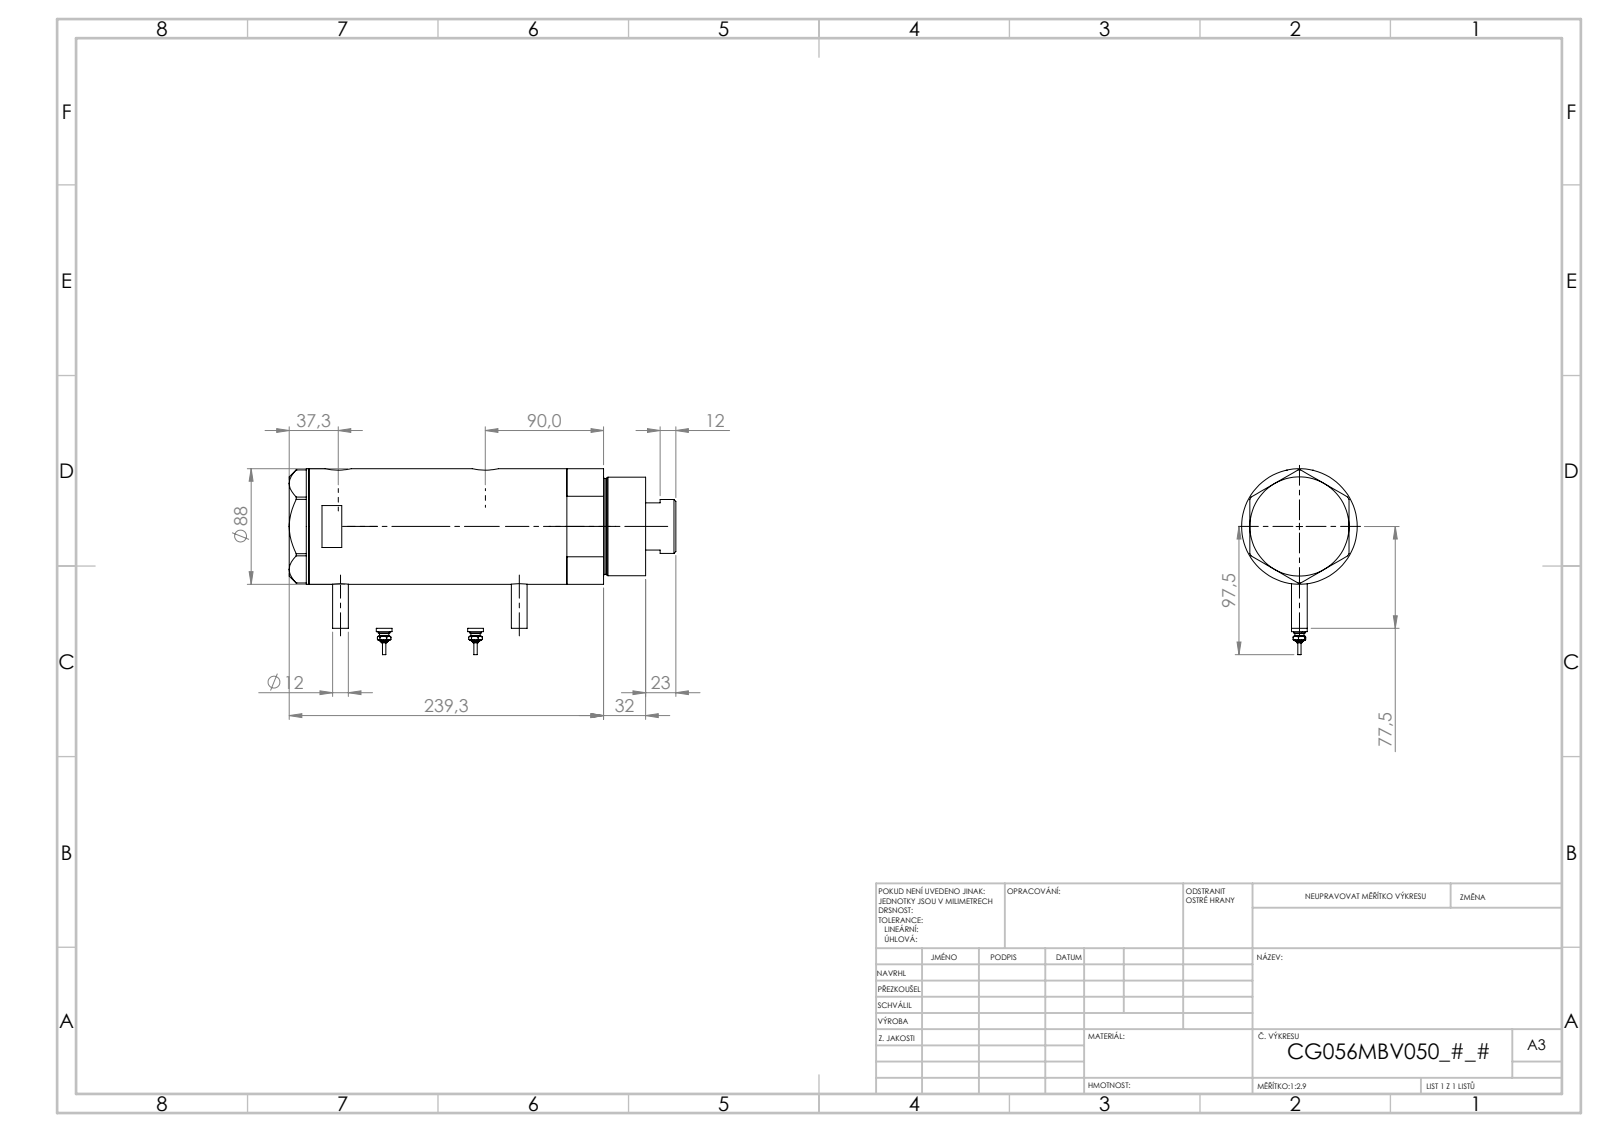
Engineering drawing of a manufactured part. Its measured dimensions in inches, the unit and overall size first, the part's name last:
Units: inches
Overall size (bounding box): 10.806 × 4.736 × 3.465
Round holes (diameter × count): ⌀0.197 ×2, ⌀0.492 ×2, ⌀0.518 ×2, ⌀0.787 ×2, ⌀0.571 ×1, ⌀1.654 ×1, ⌀1.713 ×1, ⌀2.205 ×1, ⌀2.362 ×1, ⌀3.15 ×1
Round bosses / shafts (diameter × count): ⌀0.472 ×2, ⌀0.354 ×2, ⌀0.276 ×2, ⌀0.171 ×2, ⌀0.094 ×2, ⌀3.465 ×1, ⌀2.953 ×1, ⌀2.874 ×1
Main face-to-face distances: 4.898, 1.024, 3.874, 0.591, 1.614, 5.488, 9.31, 9.9, 8.286, 4.412
Hole centre spacings: 0.067, 1.016, 3.949, 4.016, 4.965, 5.031
Volume: 86.35 in³ · Surface area: 327.7 in²
Bodies: 6 solids, 232 faces (81 planar, 77 cylindrical, 74 other)
Part name (STEP PRODUCT): V270CG_MIDDLE; V270CG_FRONT; V270CG_VC; V270CG_BACK (+1 more)
STEP written by: SolidWorks 2019 (CONFIG_CONTROL_DESIGN)
